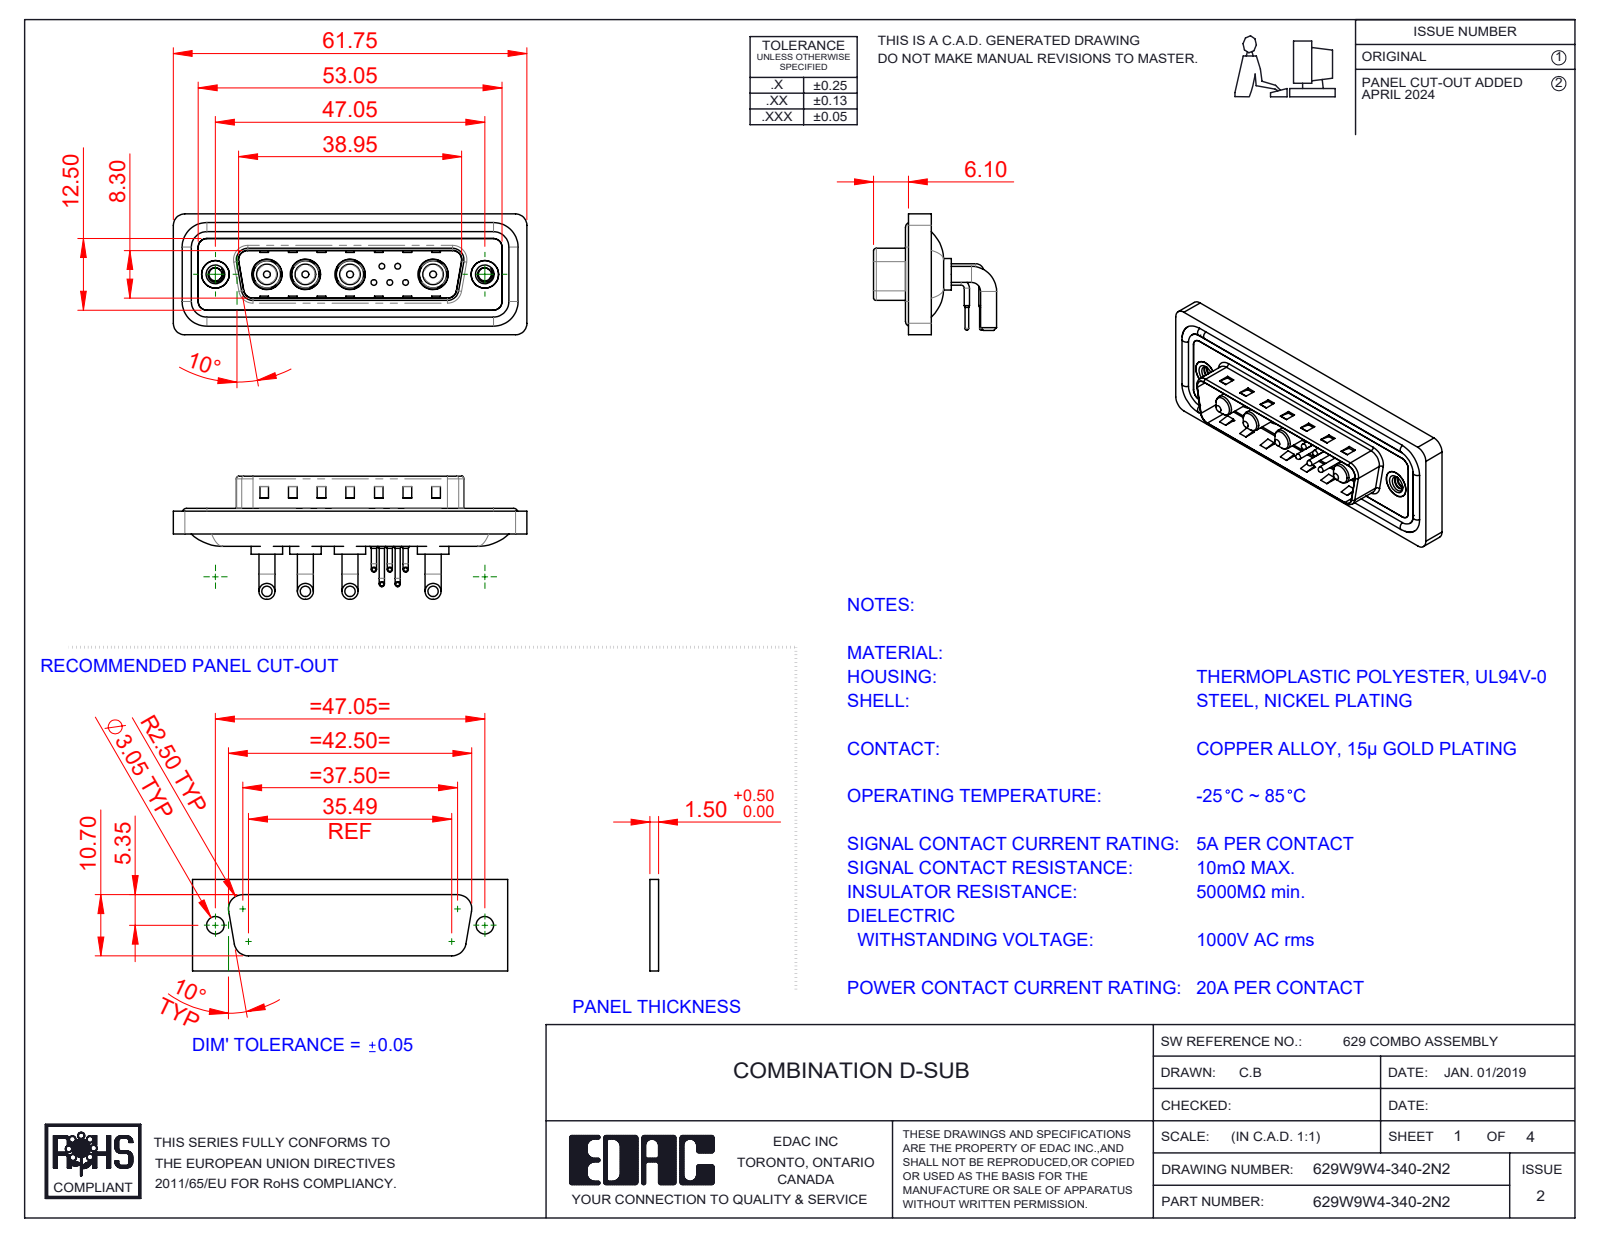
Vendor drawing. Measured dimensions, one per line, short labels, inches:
name: Power Pin_20A RA; 629Combo Waterproof Housing_25 Contacts; 629Combo Shell Front_25 Contacts; 629Combo Contact Row 1 (+5 more)
written by: SolidWorks 2023 (CONFIG_CONTROL_DESIGN)
unit: in
bodies: 20 solids, 1205 faces (569 planar, 452 cylindrical, 184 other)
size: 2.431 × 0.846 × 0.831
volume: 0.471 in³; area: 19.18 in²
holes: 5× ⌀0.03, 5× ⌀0.063, 5× ⌀0.079, 4× ⌀0.191, 4× ⌀0.209, 2× ⌀0.089, 2× ⌀0.157, 2× ⌀0.189, 2× ⌀0.197
bosses: 10× ⌀0.035, 8× ⌀0.11, 5× ⌀0.059, 5× ⌀0.039, 5× ⌀0.026, 4× ⌀0.217, 4× ⌀0.205, 4× ⌀0.187
rounds: 18× R0.059, 18× R0.079, 8× R0.02, 8× R0.063, 5× R0.04, 4× R0.01, 4× R0.024, 4× R0.026
face distances: 0.016, 0.114, 0.031, 0.161, 0.043, 0.177, 0.083, 0.063, 0.059, 0.122
hole spacings: 0.124, 0.109, 0.198, 0.571, 0.109, 0.173, 0.174, 0.197
